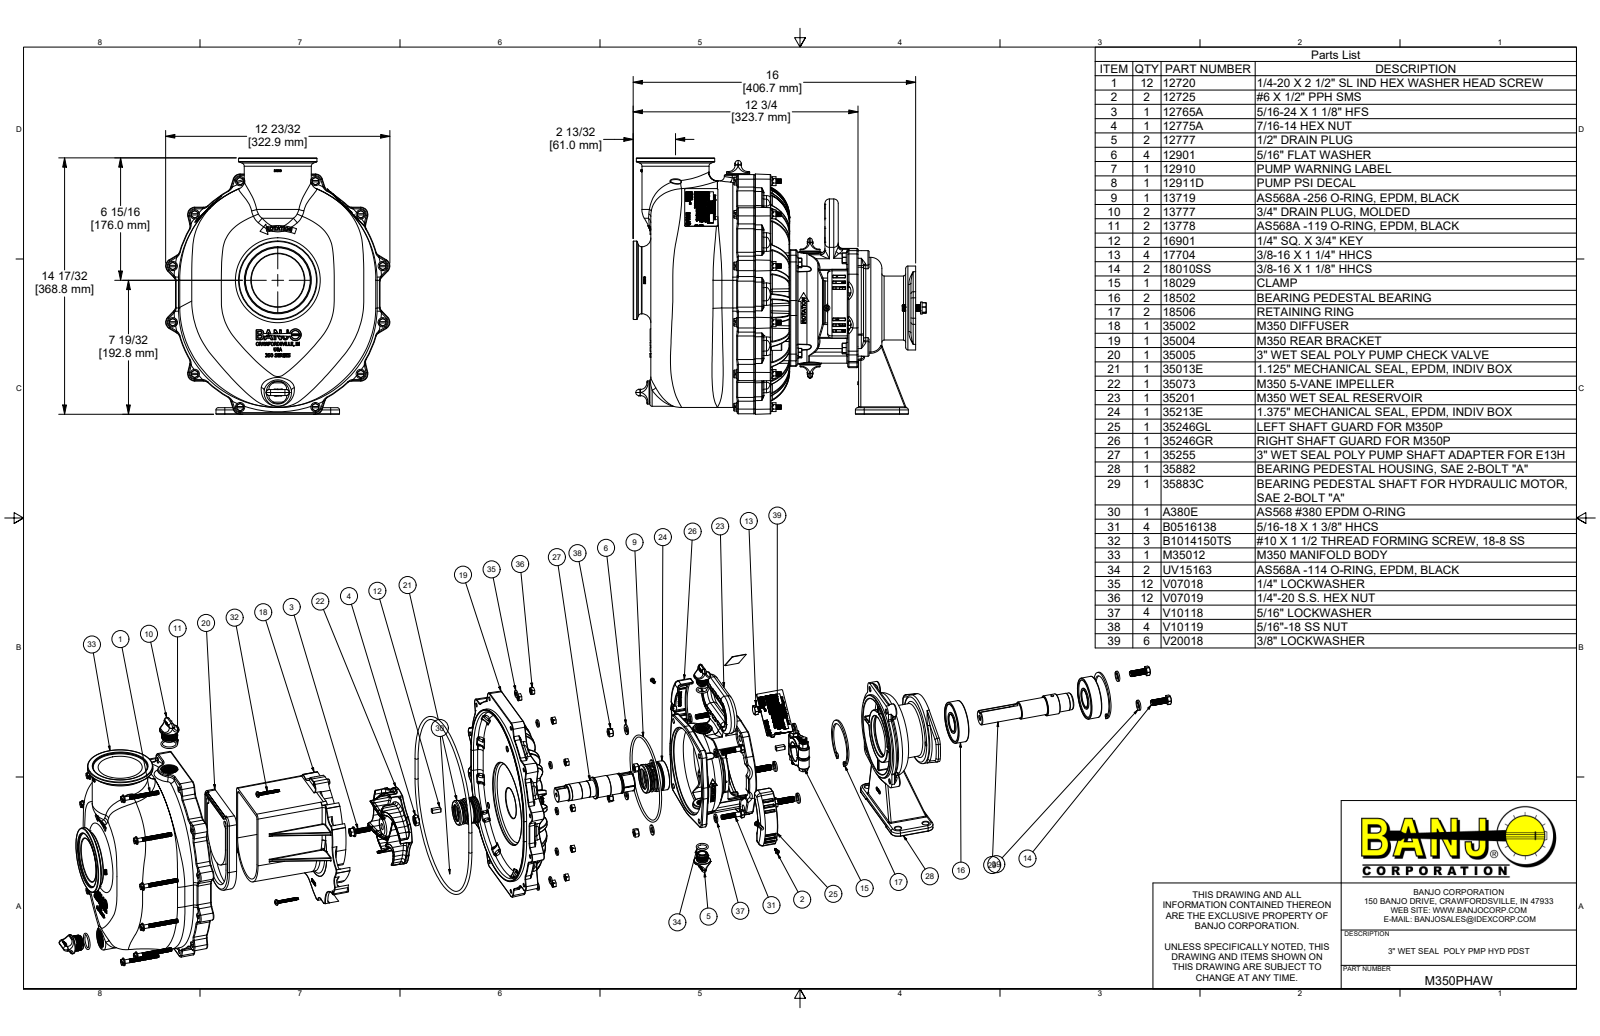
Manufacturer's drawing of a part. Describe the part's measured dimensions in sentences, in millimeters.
The part is named "M350PHAW; 17704; 18010SS; 35073 (+8 more)". Its 3-D file was written by "Autodesk Inventor 2022 (AUTOMOTIVE_DESIGN)". It is 116 solids with 24953 faces: 8623 planar, 3996 cylindrical and 12334 other. Overall it measures 421.9 by 368.8 by 322.9 millimeters. Its volume is 6 534 000 cubic millimeters and its surface area 1 777 000 square millimeters. Round holes: 12 of diameter 5, 12 of diameter 6.4, 12 of diameter 6.9, 10 of diameter 13.2, 8 of diameter 9.8, 6 of diameter 7.8, 5 of diameter 11.1, 4 of diameter 6.4, 4 of diameter 8, 4 of diameter 8.2, 4 of diameter 8.7, 4 of diameter 8.7. Round bosses or shafts: 110 of diameter 8.2, 46 of diameter 8.6, 12 of diameter 12.4, 12 of diameter 6.4, 8 of diameter 17.4, 8 of diameter 9.5, 4 of diameter 17.5, 4 of diameter 14.8. Partial cylindrical surfaces (rounded edges, fillets, slot ends): 309 of radius 0.8, 195 of radius 1.6, 88 of radius 3.2, 75 of radius 0.4, 69 of radius 2.4, 54 of radius 0.8, 52 of radius 6.4, 46 of radius 9.5. The main face-to-face distances are 10.2, 162.6, 12.7, 22.9, 127.4, 102.9, 5.1, 139.7, 6.8, 169.4. The hole center spacings are 152.5, 80.8, 238.9, 65.9, 91.7, 129.7, 134.7, 155.9.
